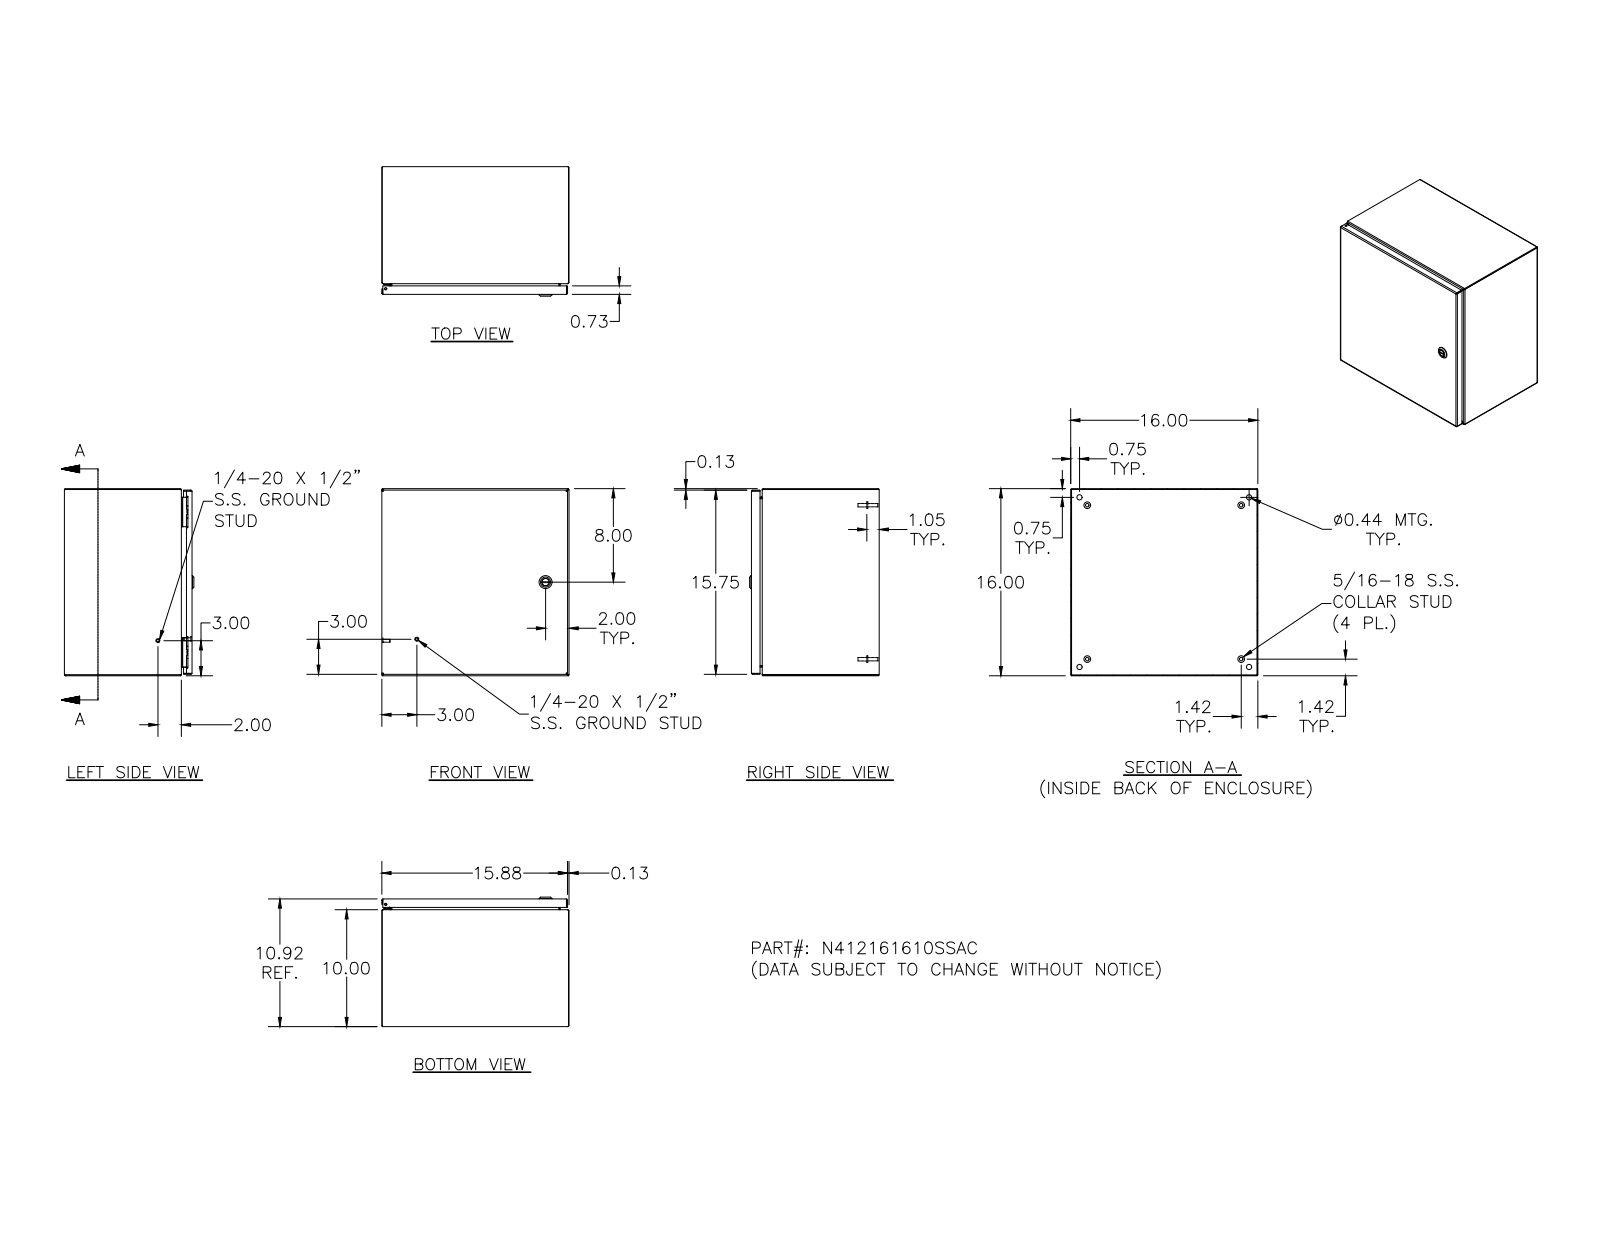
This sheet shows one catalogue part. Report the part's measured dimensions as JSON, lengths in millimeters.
{"part_name": "N412161610SSAC; N412161610SSACBKP; 388151; N4121616SSACLID (+8 more)", "step_written_by": "Autodesk Inventor 2011 (AUTOMOTIVE_DESIGN)", "units": "millimeters", "bodies": {"solids": 34, "faces": 1364, "planar": 523, "cylindrical": 497, "other": 344}, "overall_size": [406.4, 406.4, 281.3], "volume_mm3": 1560000, "surface_area_mm2": 1672000, "round_holes": [[4.8, 5], [2.4, 4], [3.9, 4], [4.2, 4], [4.4, 4], [11.1, 4], [4, 2], [4.7, 1], [5, 1], [8, 1], [10, 1], [10.2, 1]], "round_bosses_or_shafts": [[6.4, 10], [14.3, 4], [9.1, 4], [8.1, 4], [7.6, 4], [7, 4], [6.5, 4], [4.2, 4]], "partial_cylinders_radius": [[1.3, 26], [0.4, 18], [0.4, 16], [2.3, 16], [0.8, 14], [3.2, 14], [0.5, 9], [0.8, 8]], "face_to_face_distances": [1.9, 404.5, 275.4, 402.6, 406.4, 273.5, 277.3, 252.1, 23.3, 18.8], "hole_center_spacings": [304.8, 0.4, 16.8, 368.3, 0.5, 12.7, 16.5, 16.6]}
